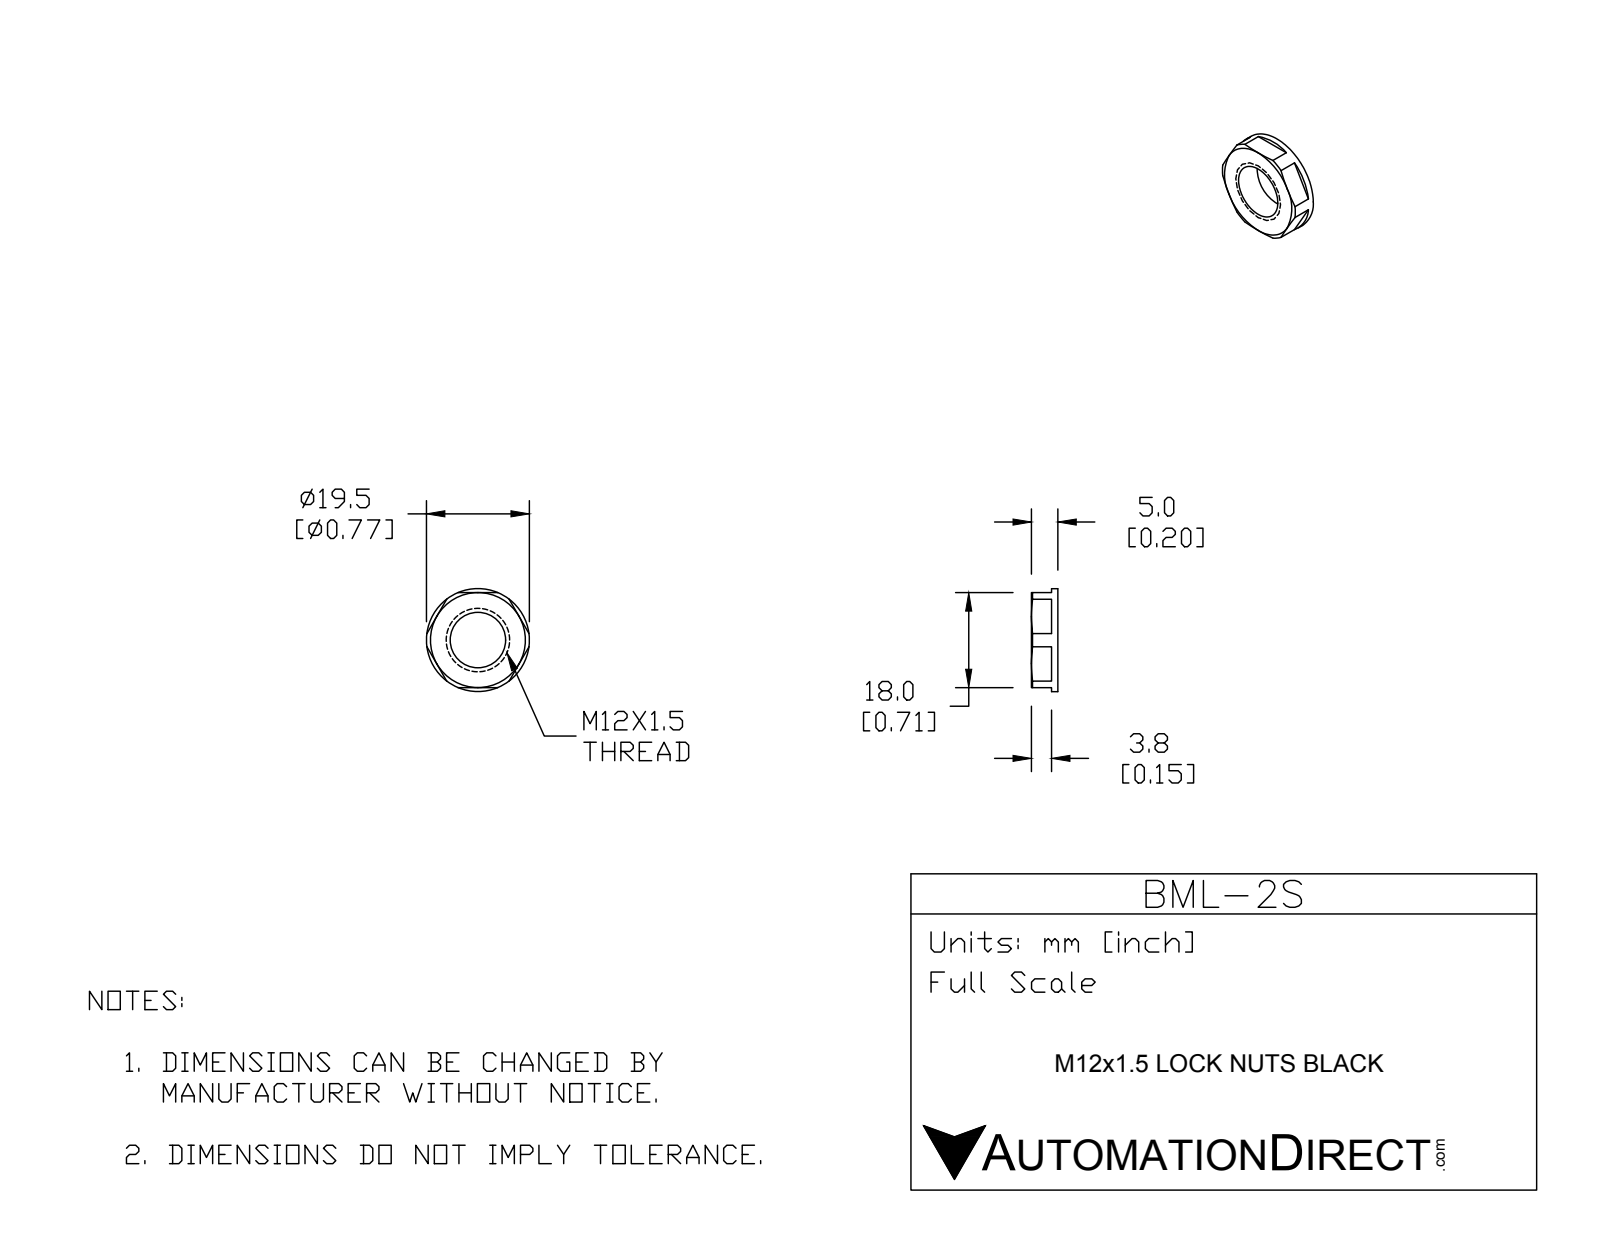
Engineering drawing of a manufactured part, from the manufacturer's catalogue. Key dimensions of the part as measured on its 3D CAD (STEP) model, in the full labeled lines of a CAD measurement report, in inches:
Part name (STEP PRODUCT): BML-2S
STEP written by: SolidWorks 2015 (CONFIG_CONTROL_DESIGN)
Units: inches
Bodies: 1 solid, 34 faces (17 planar, 10 cylindrical, 7 other)
Overall size (bounding box): 0.768 × 0.768 × 0.197
Volume: 0.059 in³ · Surface area: 1.38 in²
Round holes (diameter × count): ⌀0.059 ×3, ⌀0.413 ×1
Round bosses / shafts (diameter × count): ⌀0.768 ×1
Main face-to-face distances: 0.197, 0.709, 0.047, 0.15, 0.035, 0.185
Hole centre spacings: 0.327, 0.566
